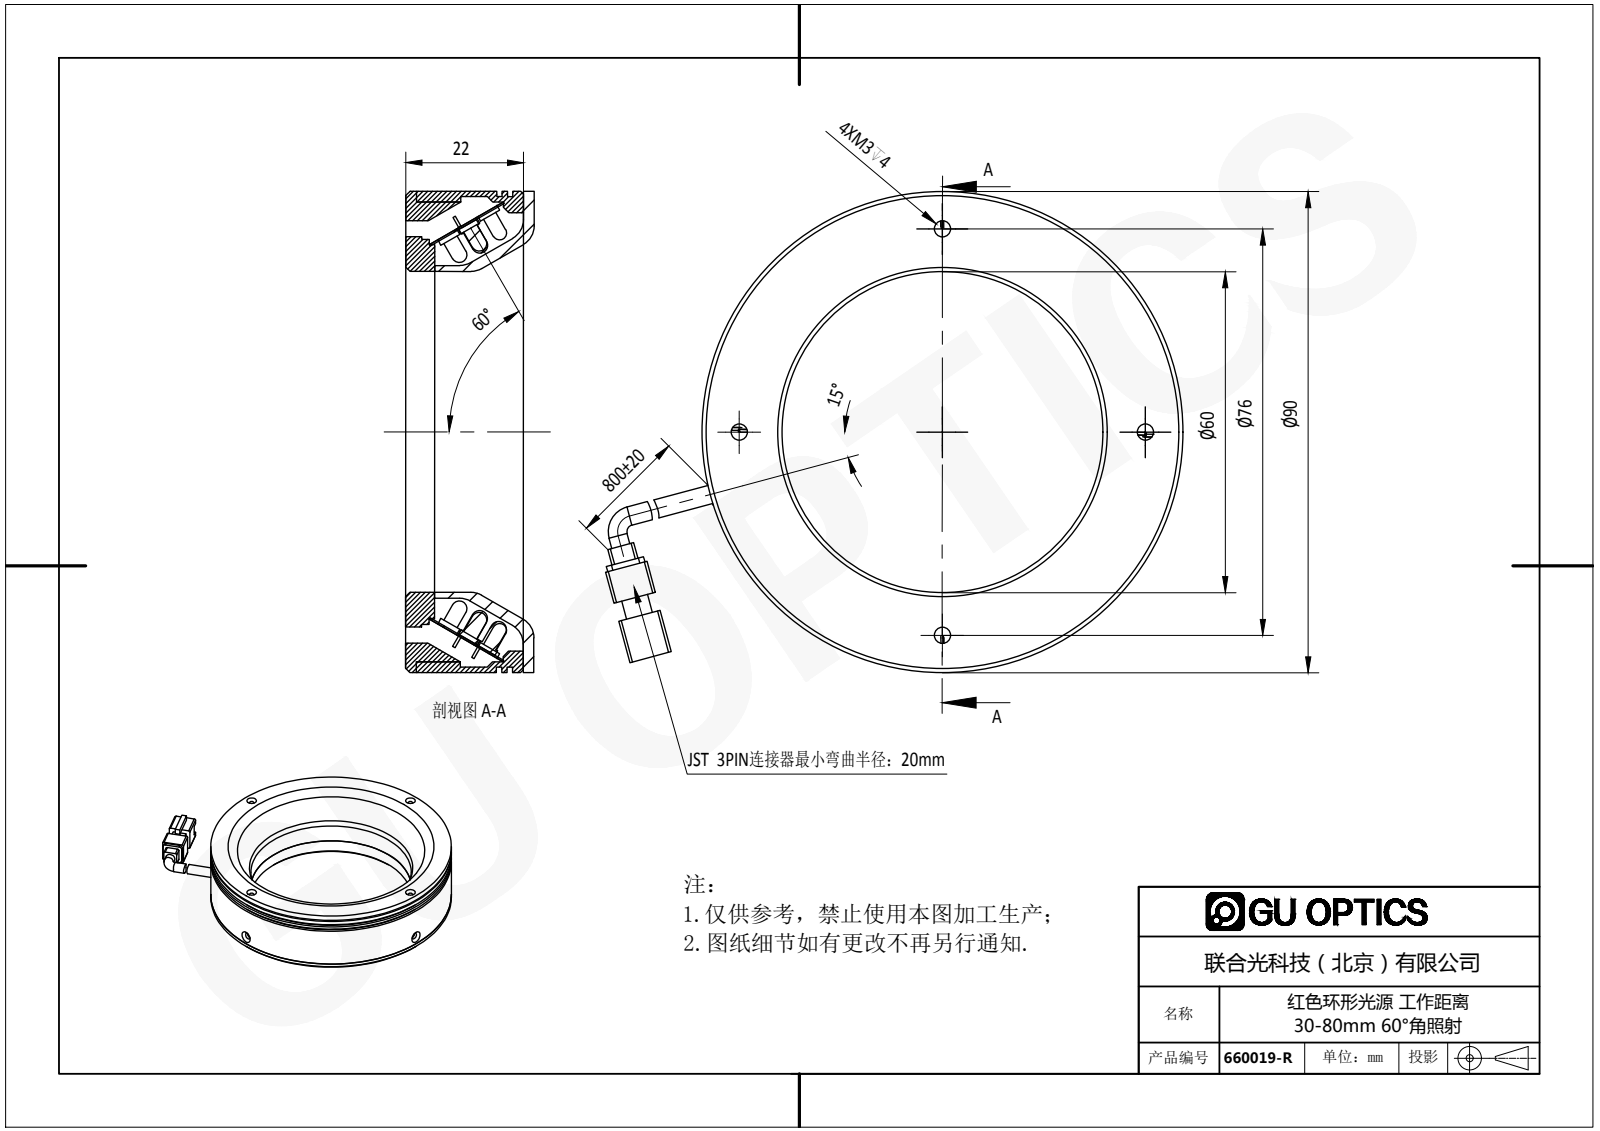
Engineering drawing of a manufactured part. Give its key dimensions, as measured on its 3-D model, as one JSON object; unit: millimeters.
{"part_name": "660019-R", "step_written_by": "SolidWorks 2016 (AUTOMOTIVE_DESIGN)", "units": "millimeters", "bodies": {"solids": 153, "faces": 2753, "planar": 1844, "cylindrical": 708, "other": 201}, "overall_size": [116.8, 90, 24.45], "volume_mm3": 46795, "surface_area_mm2": 61171, "round_holes": [[1.25, 4], [1.7, 4], [3, 4], [3.5, 3], [2, 2], [2.4, 2], [60, 1], [82, 1], [86, 1]], "round_bosses_or_shafts": [[3.8, 147], [3, 147], [3.5, 2], [90, 1], [88, 1], [72, 1], [70, 1], [62.2, 1]], "partial_cylinders_radius": [[0.5, 8], [1, 4], [1.65, 1], [5, 1]], "face_to_face_distances": [2, 22, 1, 24, 3, 20, 5.4, 16.6, 18.6, 3.4], "hole_center_spacings": [30.84, 73.93, 38, 42, 53.74, 59.4, 76, 84]}
